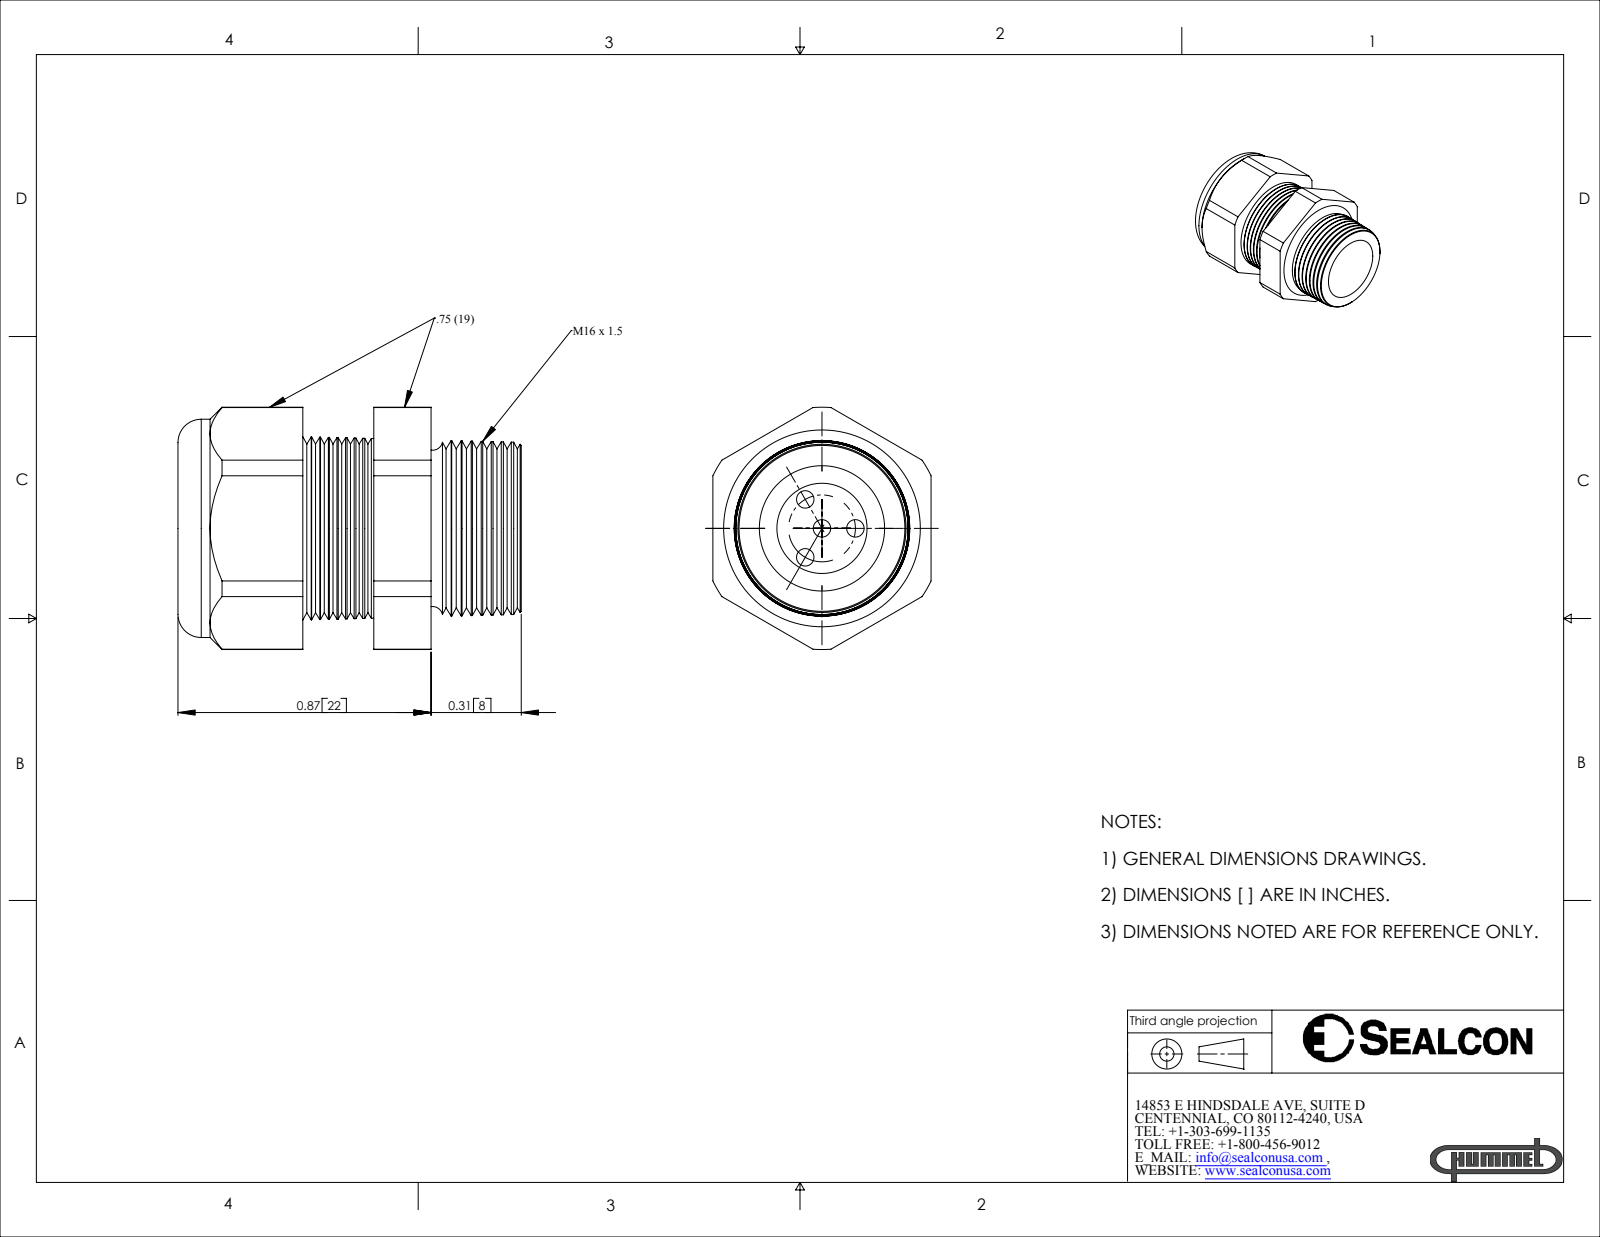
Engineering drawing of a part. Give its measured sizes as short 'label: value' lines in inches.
name: CD16M9-BK
written by: SolidWorks 2007 (CONFIG_CONTROL_DESIGN)
unit: in
bodies: 2 solids, 158 faces (20 planar, 28 cylindrical, 110 other)
size: 1.18 × 0.833 × 0.75
volume: 0.336 in³; area: 6.185 in²
holes: 4× ⌀0.06, 1× ⌀0.29, 1× ⌀0.31
bosses: 1× ⌀0.75
rounds: 1× R0.416
face distances: 0.75, 0.673, 0.75, 0.429, 0.244, 0.87, 0.441, 0.197, 1.18, 0.751
hole spacings: 0.115, 0.199
